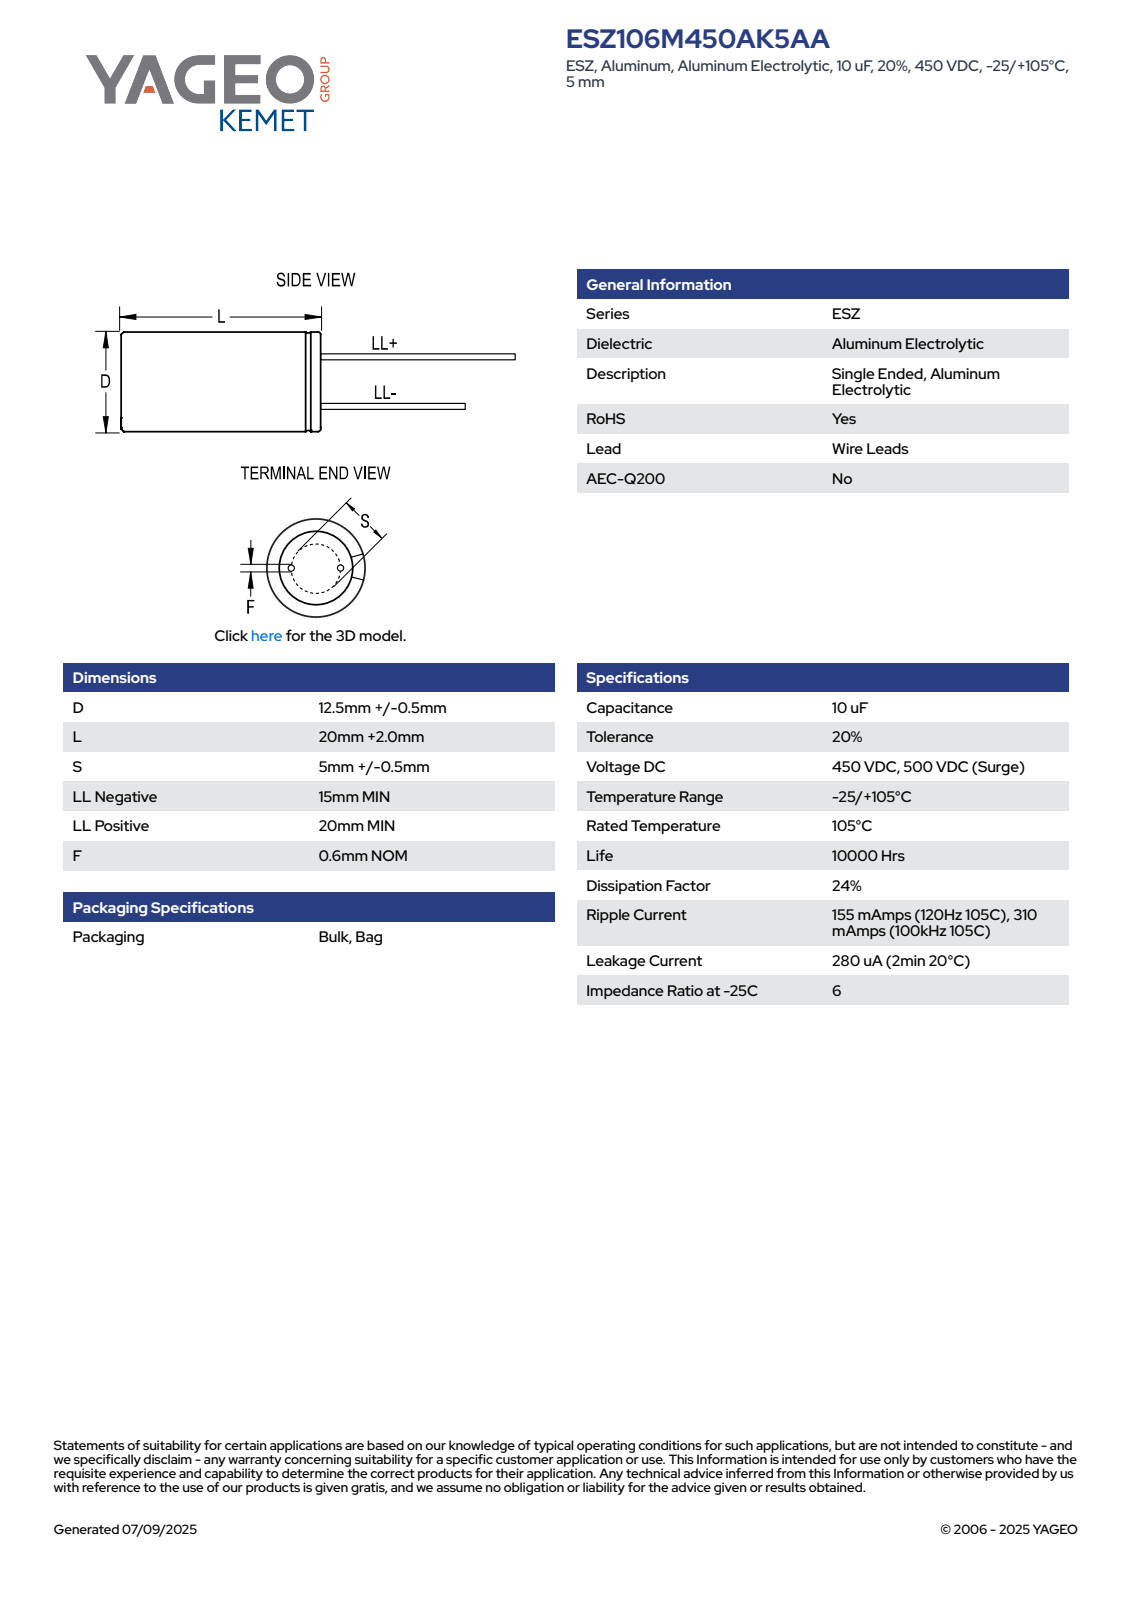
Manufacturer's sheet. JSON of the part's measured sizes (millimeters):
{"part_name": "CAR_KLP_12.5X20_D13L22S5F0.6", "step_written_by": "SolidWorks 2014 (AUTOMOTIVE_DESIGN)", "units": "millimeters", "bodies": {"solids": 4, "faces": 75, "planar": 61, "cylindrical": 8, "other": 6}, "overall_size": [42.01, 13, 13], "volume_mm3": 2907, "surface_area_mm2": 1268, "round_bosses_or_shafts": [[0.6, 2], [13, 1]], "face_to_face_distances": [22, 22.01, 37.01, 42.01, 37, 42, 15, 20, 5, 1.75]}
